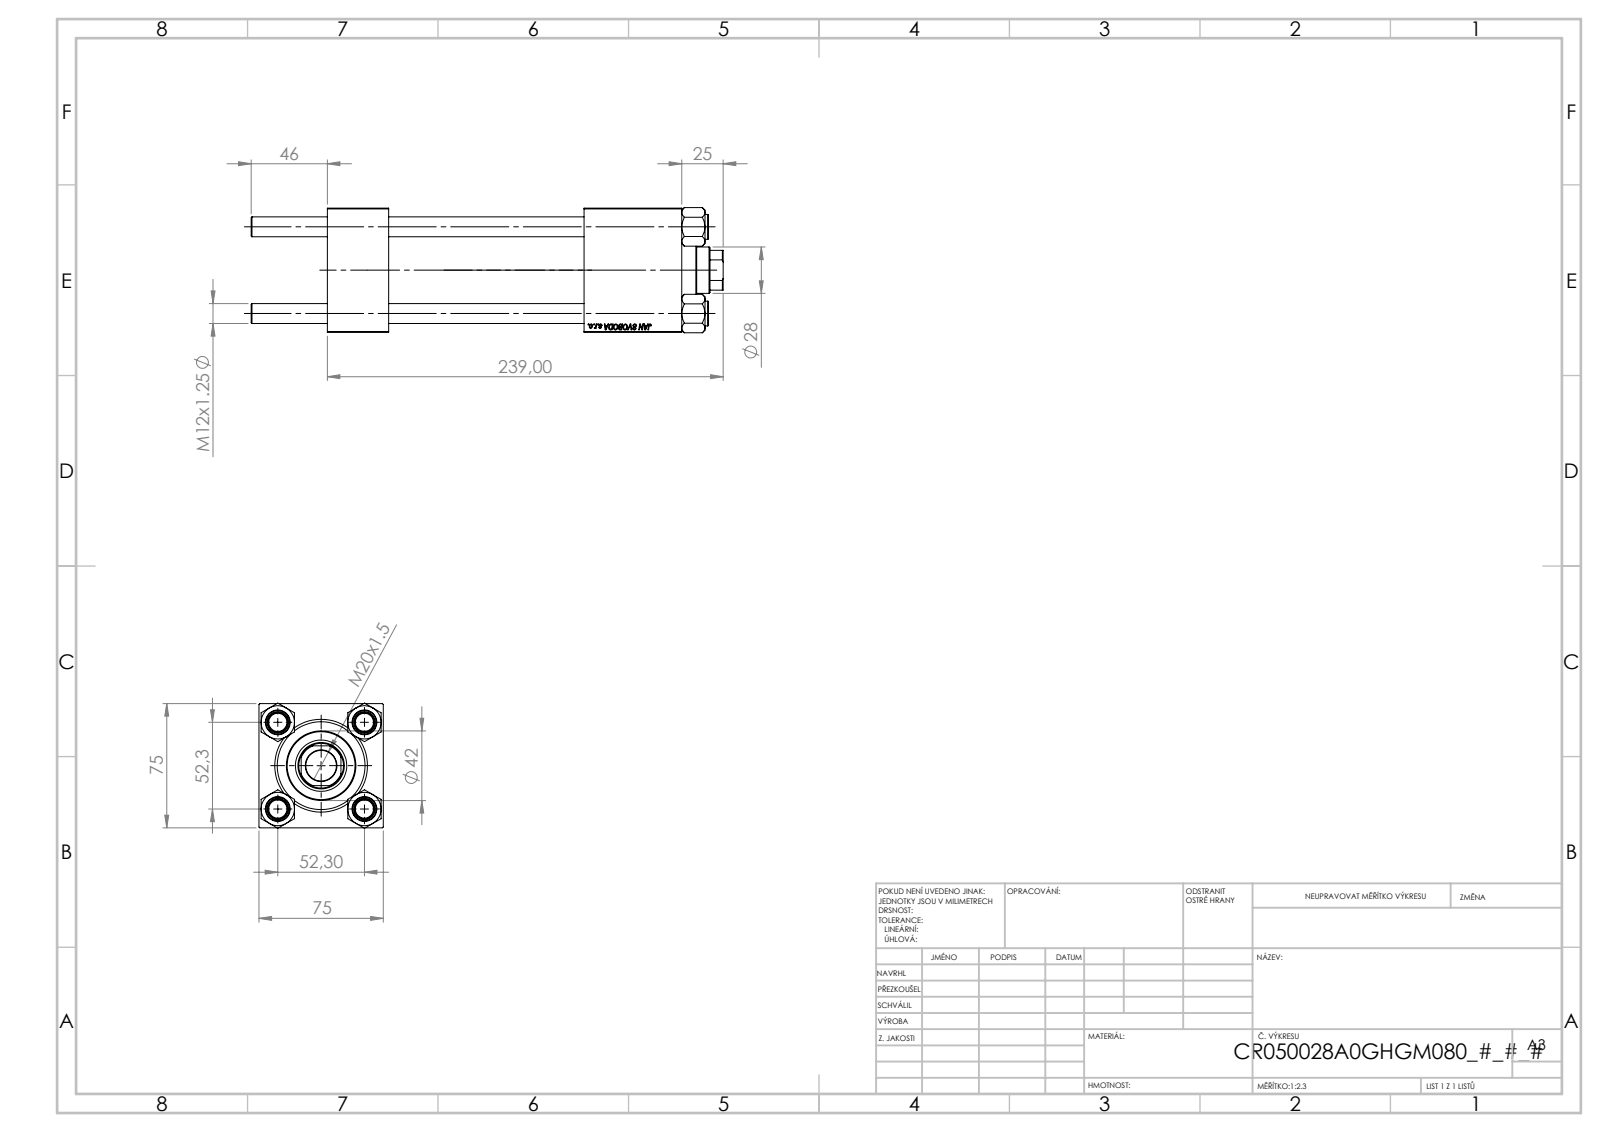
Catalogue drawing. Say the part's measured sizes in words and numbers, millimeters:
The part is named "NUT_M5; CR025_012_A_0_G_A_G_M_020_+#_##_TYCINKA; V215CR_VCP; V215_VC_A (+1 more)". Its 3-D file was written by "SolidWorks 2019 (CONFIG_CONTROL_DESIGN)". It is 11 solids with 1134 faces: 520 planar, 78 cylindrical and 536 other. Overall it measures 285 by 75.54 by 75 millimeters. Its volume is 796 270 cubic millimeters and its surface area 201 695 square millimeters. Round holes: 4 of diameter 12, 2 of diameter 7, 2 of diameter 20.96, 2 of diameter 30, 1 of diameter 18.5, 1 of diameter 28, 1 of diameter 31, 1 of diameter 41, 1 of diameter 50, 1 of diameter 53. Round bosses or shafts: 4 of diameter 15, 1 of diameter 56, 1 of diameter 42. Partial cylindrical surfaces (rounded edges, fillets, slot ends): 1 of radius 13.5. The main face-to-face distances are 75, 37, 214, 177, 155, 118, 59, 185.3, 148.3, 30.3. The hole center spacings are 36.98, 52.3, 73.96, 153.5.
